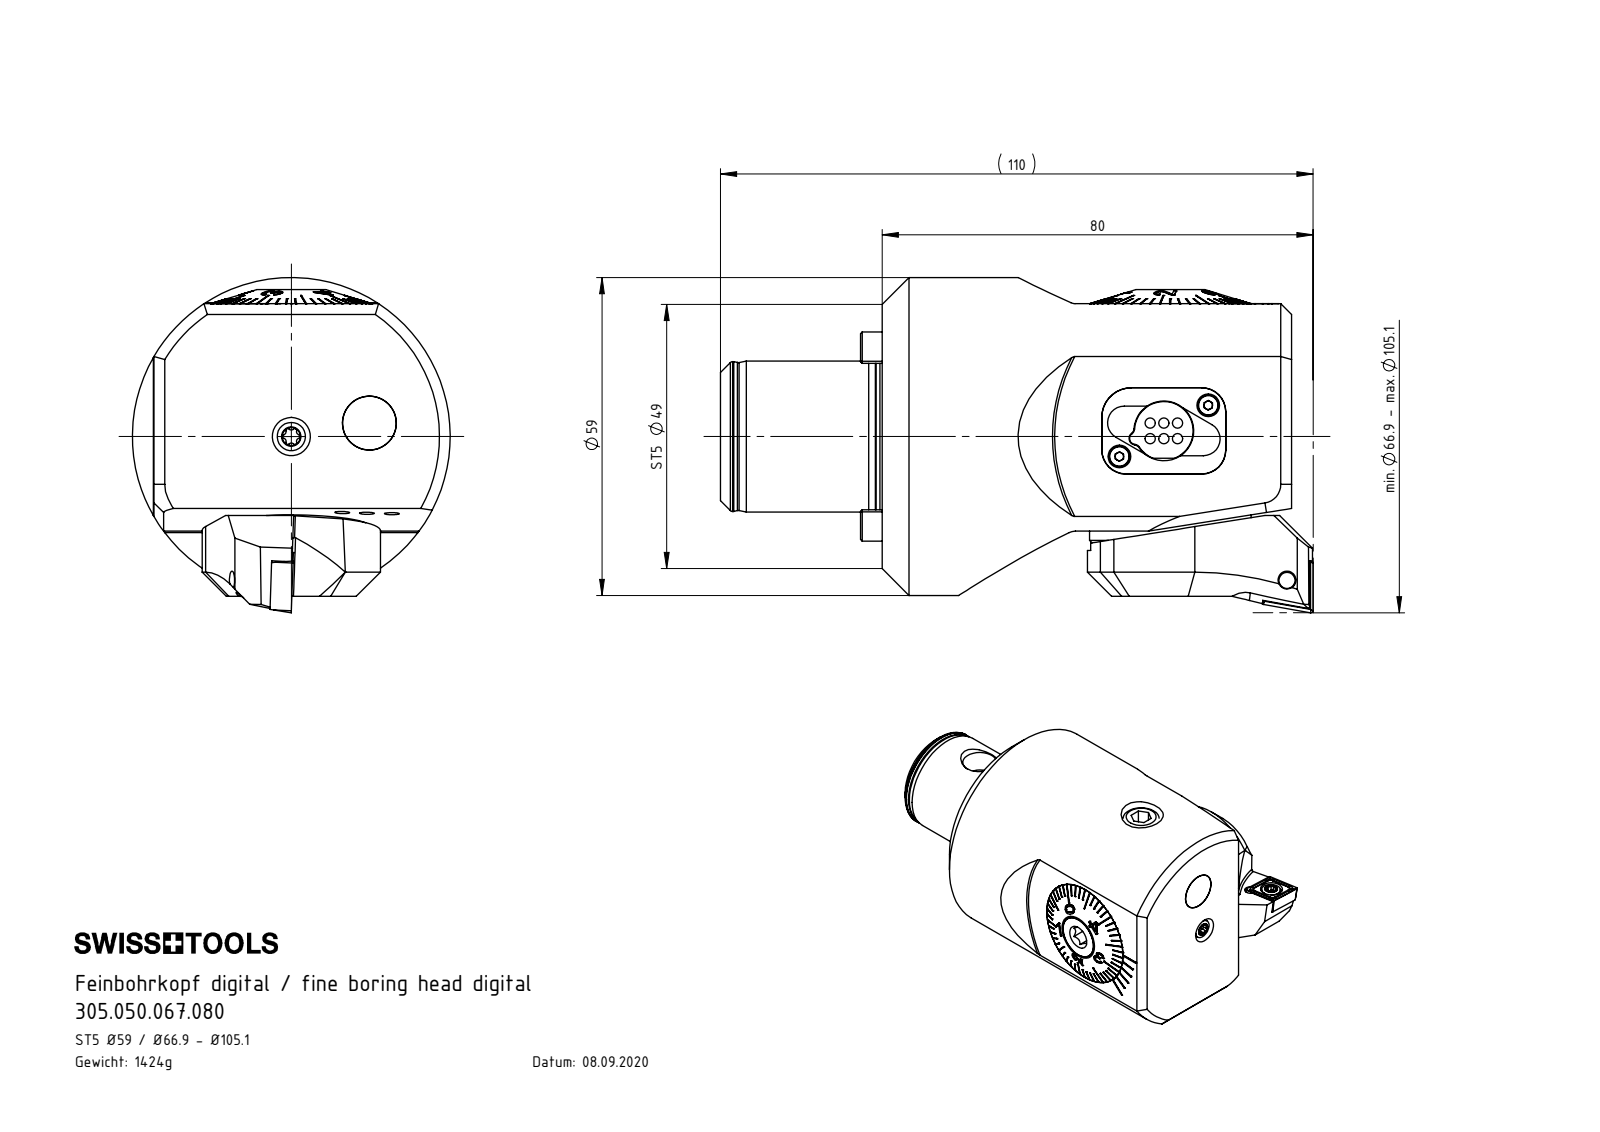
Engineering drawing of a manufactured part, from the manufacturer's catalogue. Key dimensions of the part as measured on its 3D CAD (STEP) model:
Part name (STEP PRODUCT): A55-BG3.011.033_A_gekrzt; ST5-F55.DA1.080_A; F55-WCB.001.013; Klebstoff D10 (+8 more)
STEP written by: SolidWorks 2017 (CONFIG_CONTROL_DESIGN)
Units: millimetres
Bodies: 29 solids, 1201 faces (469 planar, 322 cylindrical, 410 other)
Overall size (bounding box): 110 × 65.75 × 55
Volume: 180 556 mm³ · Surface area: 52 107 mm²
Round holes (diameter × count): ⌀3.3 ×9, ⌀4.2 ×3, ⌀1.6 ×2, ⌀2.2 ×2, ⌀4 ×2, ⌀8.5 ×2, ⌀4.4 ×1, ⌀5 ×1, ⌀6.1 ×1, ⌀6.8 ×1, ⌀8 ×1, ⌀10 ×1
Round bosses / shafts (diameter × count): ⌀1.9 ×6, ⌀10 ×2, ⌀5.25 ×2, ⌀4 ×2, ⌀3.8 ×2, ⌀2 ×2, ⌀55 ×1, ⌀29.98 ×1
Partial cylindrical surfaces — rounded edges, fillets, slot ends (radius × count): R0.34 ×12, R0.59 ×12, R0.5 ×8, R1.2 ×8, R1.1 ×6, R4.5 ×4, R3.2 ×3, R4.4 ×3
Main face-to-face distances: 76, 4, 3.7, 2, 8.15, 2.5, 2.8, 47.85, 10, 36
Hole centre spacings: 9.52, 16.9, 22.27, 5.73, 5.86, 9.74, 14.5, 19.04
